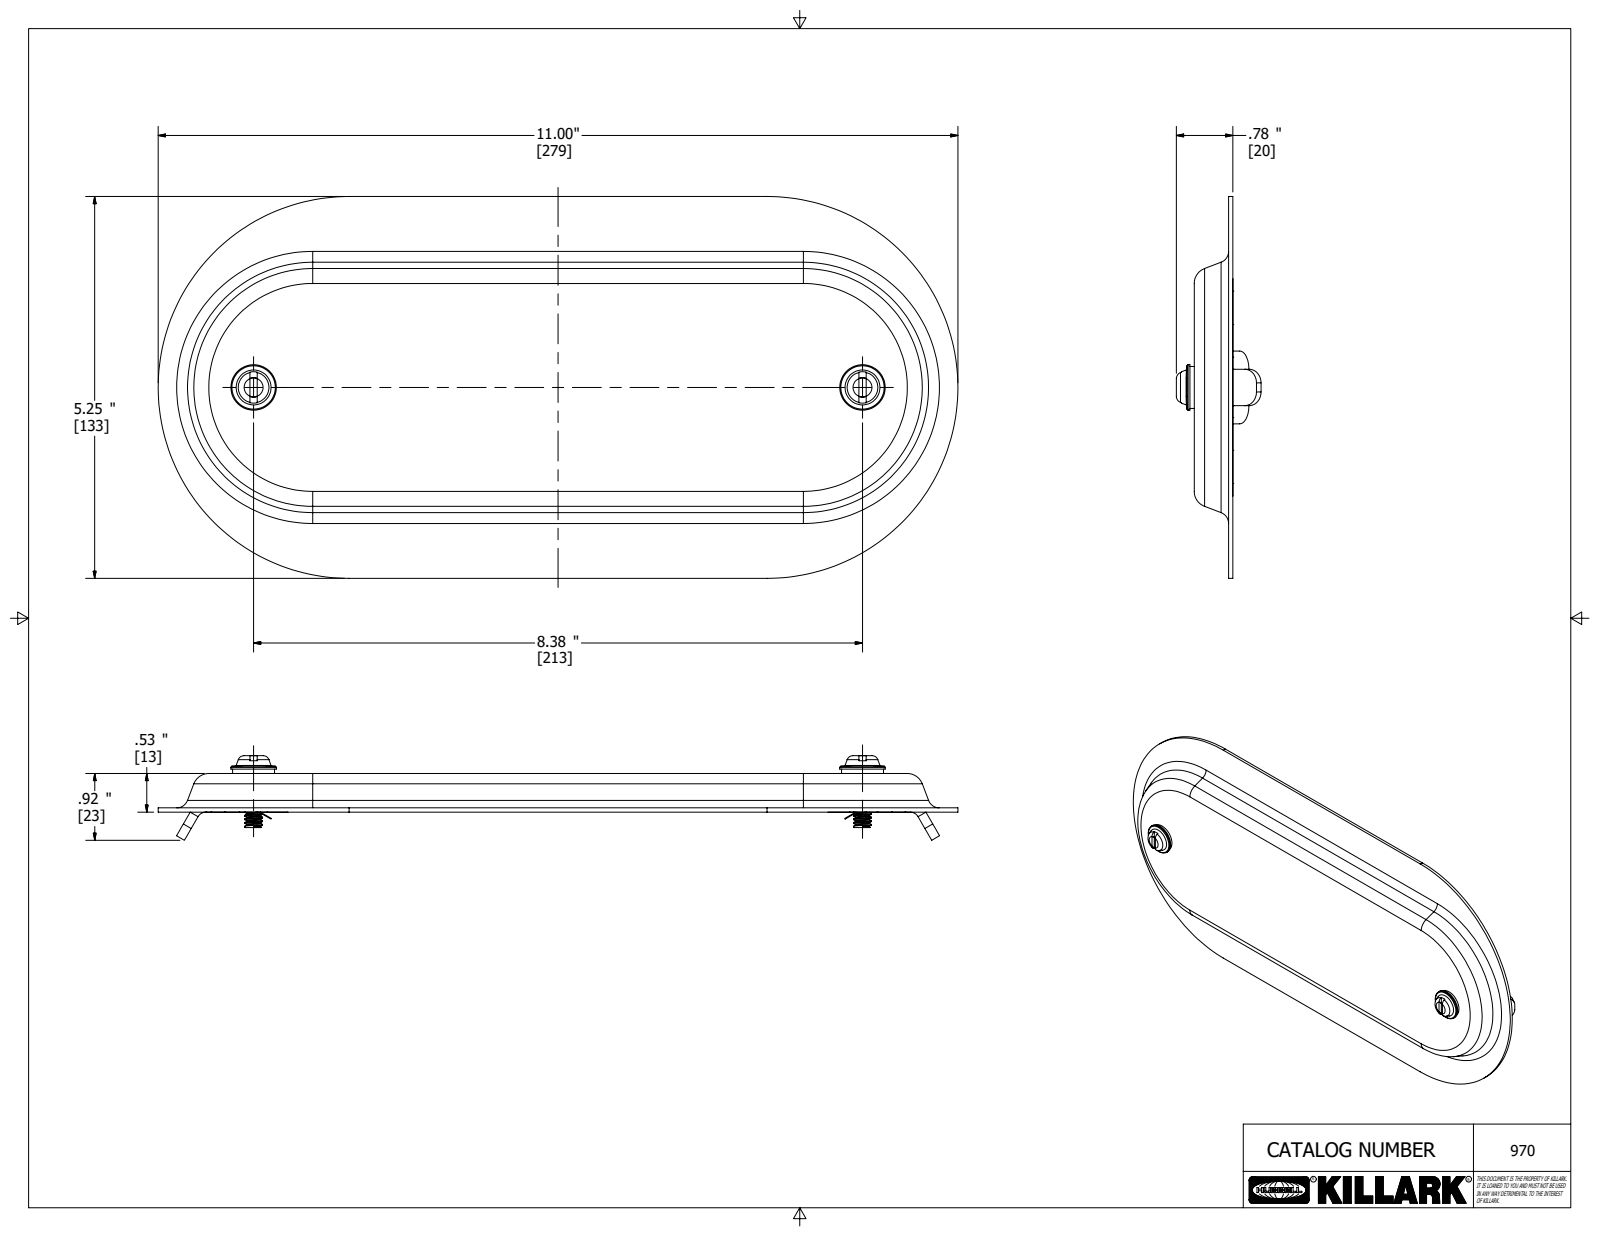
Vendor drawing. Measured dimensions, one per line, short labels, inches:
name: 970; 18397; 18038CABB; 17953
written by: Autodesk Inventor 2018 (AUTOMOTIVE_DESIGN)
unit: in
bodies: 5 solids, 156 faces (76 planar, 52 cylindrical, 28 other)
size: 11 × 5.25 × 1.164
volume: 4.628 in³; area: 139.4 in²
holes: 2× ⌀0.25, 2× ⌀0.344
bosses: 2× ⌀0.625, 2× ⌀0.577, 2× ⌀0.246, 2× ⌀0.196
rounds: 8× R0.187, 4× R0.125, 4× R0.16, 4× R0.22, 4× R0.25, 4× R0.5, 4× R0.875, 2× R0.219
face distances: 0.062, 0.469, 0.531, 0.059, 0.41, 0.472, 0.125, 0.066, 0.344, 0.406
hole spacings: 8.375
